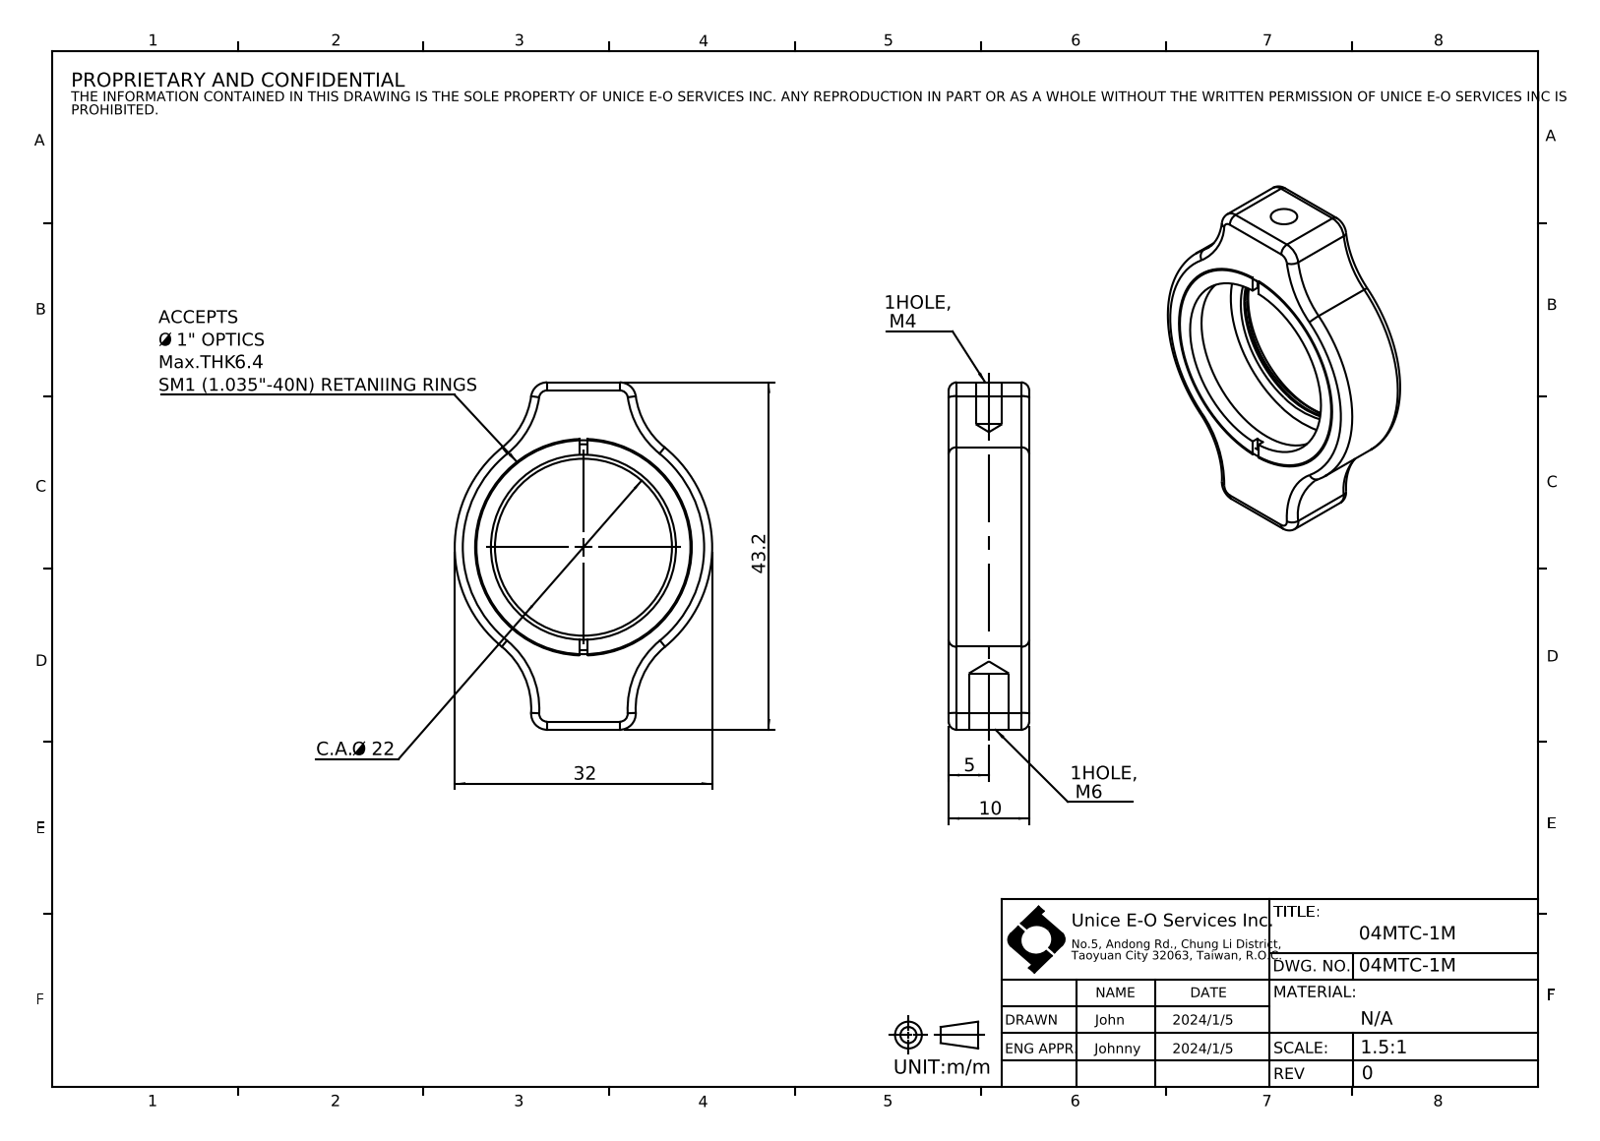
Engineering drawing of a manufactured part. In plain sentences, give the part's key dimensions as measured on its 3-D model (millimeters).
The part is named "04MTC-1M". Its 3-D file was written by "SolidWorks 2016 (CONFIG_CONTROL_DESIGN)". It is 3 solids with 89 faces: 16 planar, 33 cylindrical and 40 other. Overall it measures 43.2 by 32 by 10 millimeters. Its volume is 4 846 cubic millimeters and its surface area 4 178 square millimeters. Round holes: 1 of diameter 3.3, 1 of diameter 5, 1 of diameter 22, 1 of diameter 23, 1 of diameter 25.6. Round bosses or shafts: 1 of diameter 26.93, 1 of diameter 25.5. Partial cylindrical surfaces (rounded edges, fillets, slot ends): 4 of radius 1, 4 of radius 2, 4 of radius 10, 1 of radius 16. The main face-to-face distances are 10, 1, 9, 8, 7, 2, 1.6, 0.6, 6.4, 8.4.
